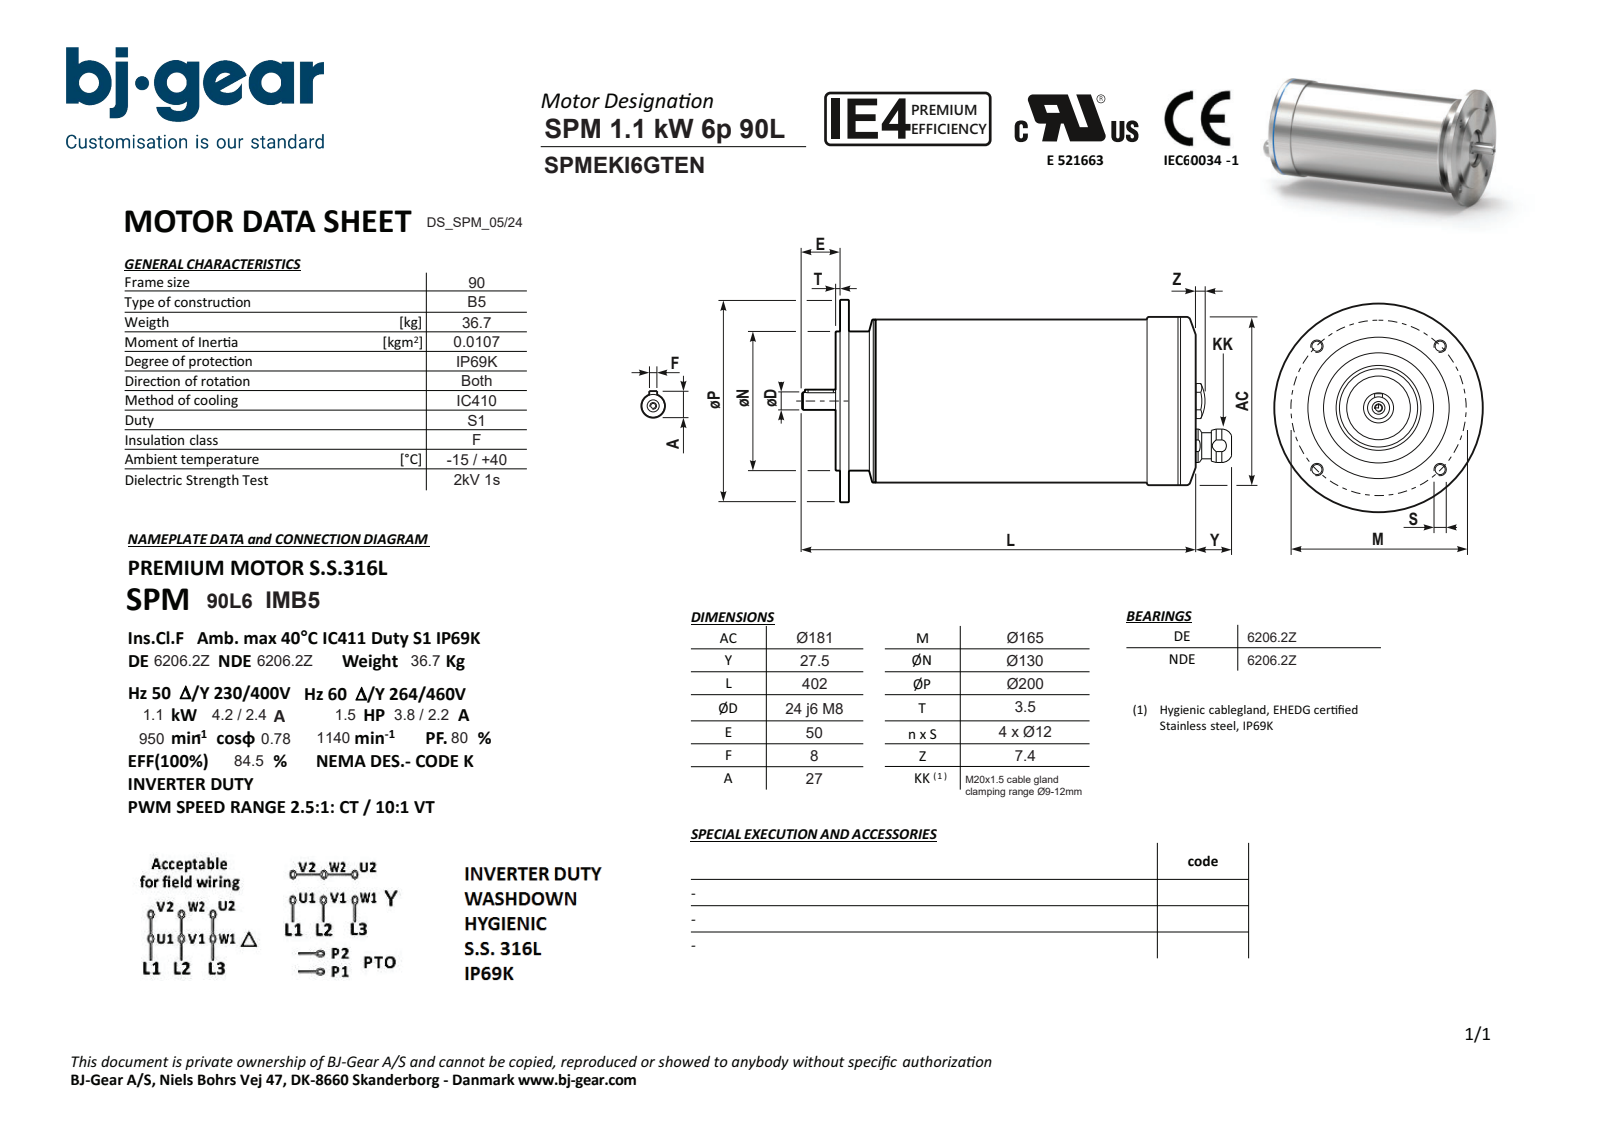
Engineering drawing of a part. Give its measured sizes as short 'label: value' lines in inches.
name: SPMEKI6GTENN4KSA1-N---NNN
written by: Solid Edge (AUTOMOTIVE_DESIGN)
unit: in
bodies: 1 solid, 86 faces (31 planar, 30 cylindrical, 25 other)
size: 16.909 × 7.874 × 7.874
volume: 526.8 in³; area: 438.2 in²
holes: 4× ⌀0.472, 1× ⌀0.194, 1× ⌀0.276, 1× ⌀0.331, 1× ⌀0.528, 1× ⌀3.346
bosses: 1× ⌀7.874, 1× ⌀7.126, 1× ⌀7.125, 1× ⌀7.008, 1× ⌀7.007, 1× ⌀5.591, 1× ⌀5.118, 1× ⌀1.181
rounds: 2× R0.157, 1× R0.504
face distances: 13.858, 0.315, 13.543, 13.996, 0.453, 0.138, 0.236, 0.079, 13.622, 0.374
hole spacings: 3.248, 4.594, 2.301, 5.019, 6.496, 2.165
